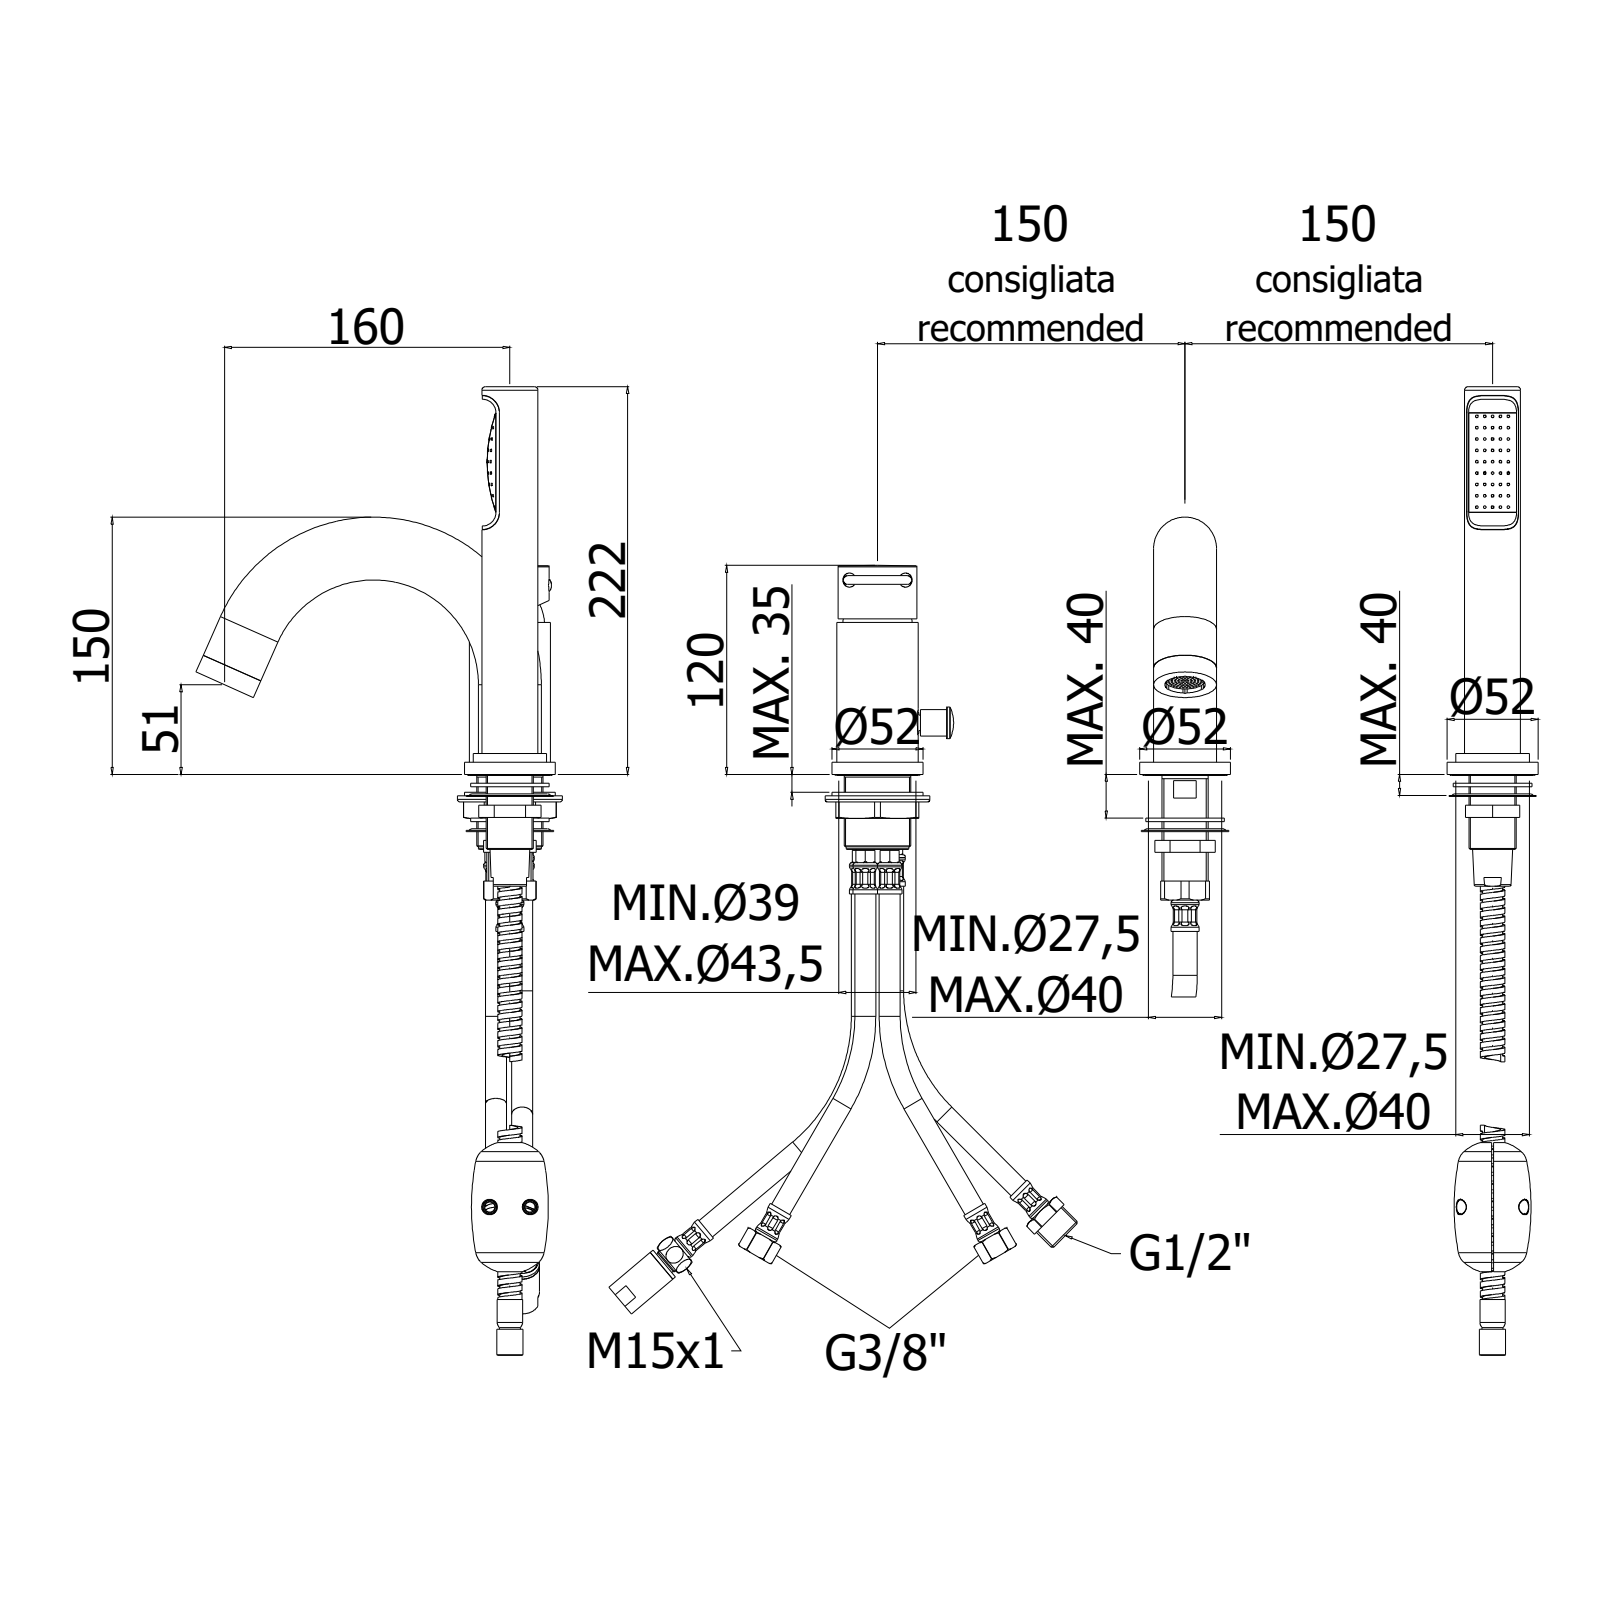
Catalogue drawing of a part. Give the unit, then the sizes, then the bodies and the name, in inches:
Units: inches
Overall size (bounding box): 13.858 × 8.74 × 8.103
Round holes (diameter × count): ⌀0.02 ×61, ⌀0.059 ×45, ⌀0.276 ×6, ⌀1.937 ×3, ⌀0.157 ×2, ⌀0.748 ×2, ⌀1.055 ×2, ⌀1.071 ×2, ⌀1.299 ×2, ⌀1.339 ×2, ⌀0.118 ×1, ⌀0.122 ×1
Round bosses / shafts (diameter × count): ⌀2.047 ×3, ⌀1.74 ×3, ⌀0.197 ×3, ⌀1.417 ×2, ⌀1.335 ×2, ⌀1.831 ×1, ⌀1.772 ×1, ⌀1.693 ×1
Partial cylindrical surfaces — rounded edges, fillets, slot ends (radius × count): R0.01 ×30, R0.02 ×27, R0.006 ×11, R0.012 ×4, R0.039 ×2, R0.061 ×2, R0.307 ×2, R0.386 ×2
Main face-to-face distances: 0.276, 0.079, 0.197, 0.394, 0.472, 0.098, 8.661, 0.118, 0.02, 4.531
Hole centre spacings: 0.226, 0.15, 0.311, 0.542, 0.075, 0.788, 0.256, 0.512
Volume: 18.02 in³ · Surface area: 306.5 in²
Bodies: 4 solids, 2106 faces (1211 planar, 639 cylindrical, 256 other)
Part name (STEP PRODUCT): JK040LCR
STEP written by: CREO PARAMETRIC BY PTC INC, 2020044 (CONFIG_CONTROL_DESIGN)
